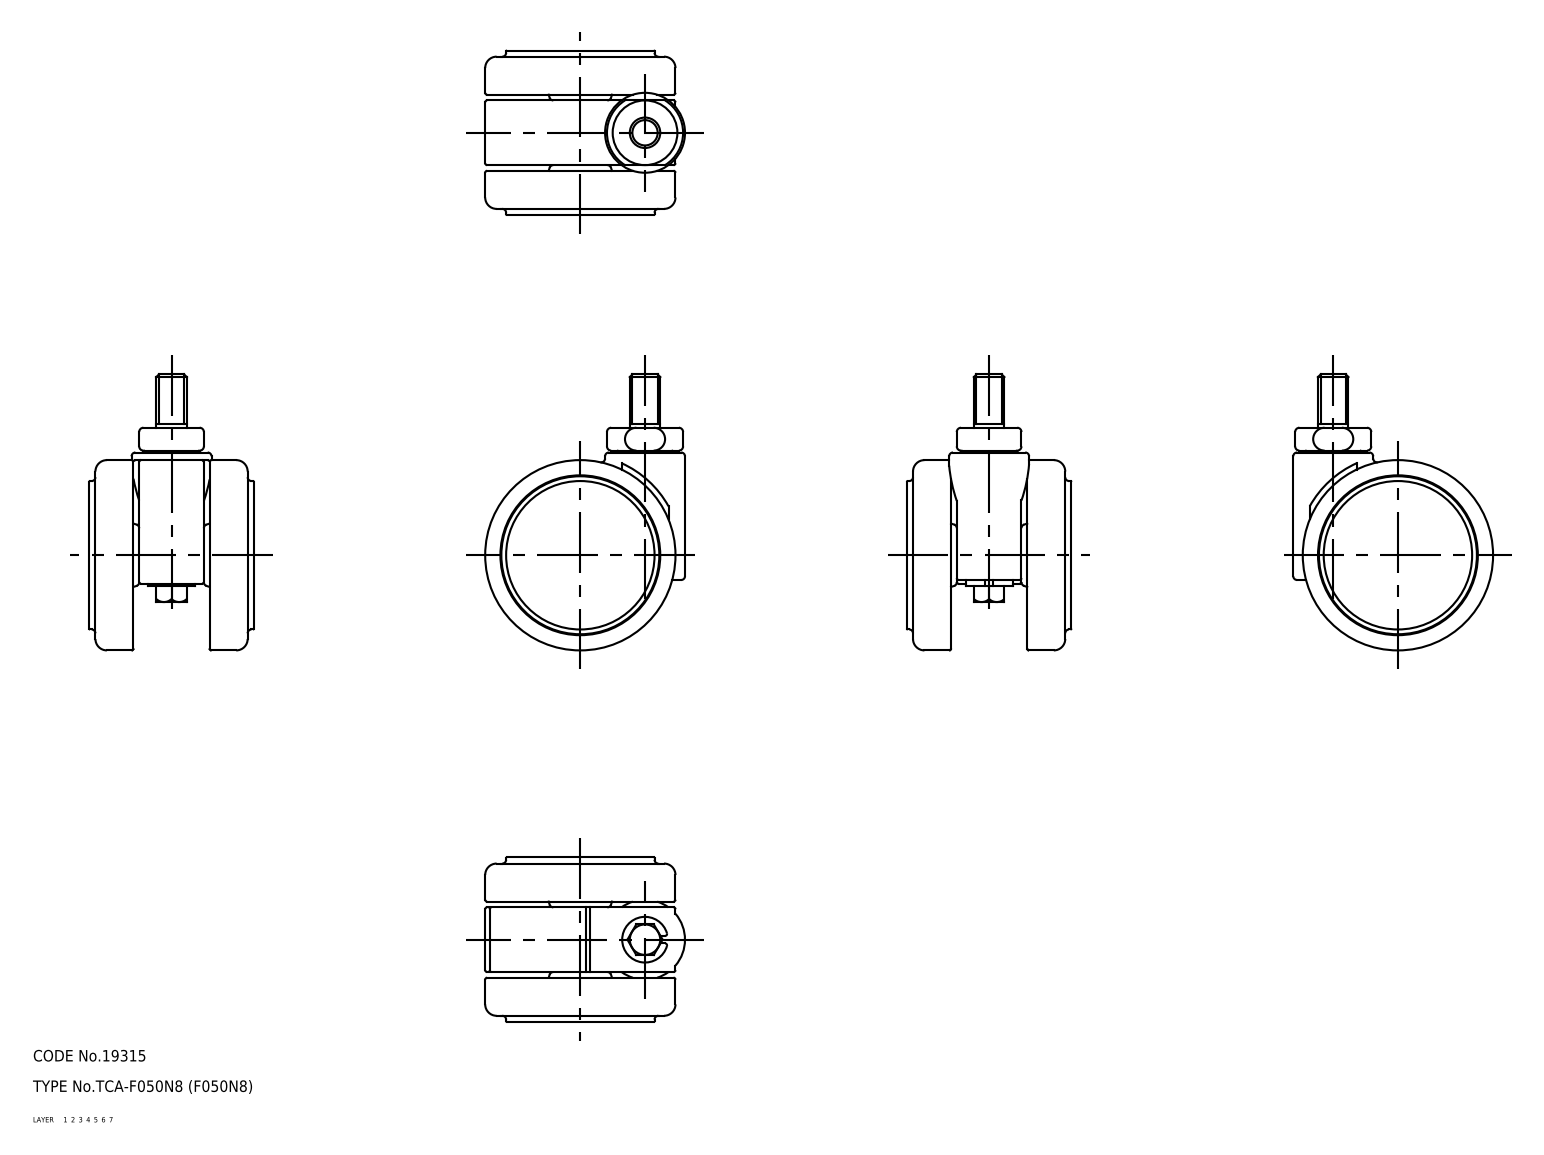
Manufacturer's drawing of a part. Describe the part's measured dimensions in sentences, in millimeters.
The part is named "67117956; 67117969; 67117982; 67117995". Its 3-D file was written by "CADfix (AUTOMOTIVE_DESIGN)". It is 4 solids with 131 faces: 0 planar, 0 cylindrical and 131 other. Overall it measures 72.5 by 52.5 by 43.2 millimeters. Its volume is 61 151 cubic millimeters and its surface area 21 268 square millimeters.
